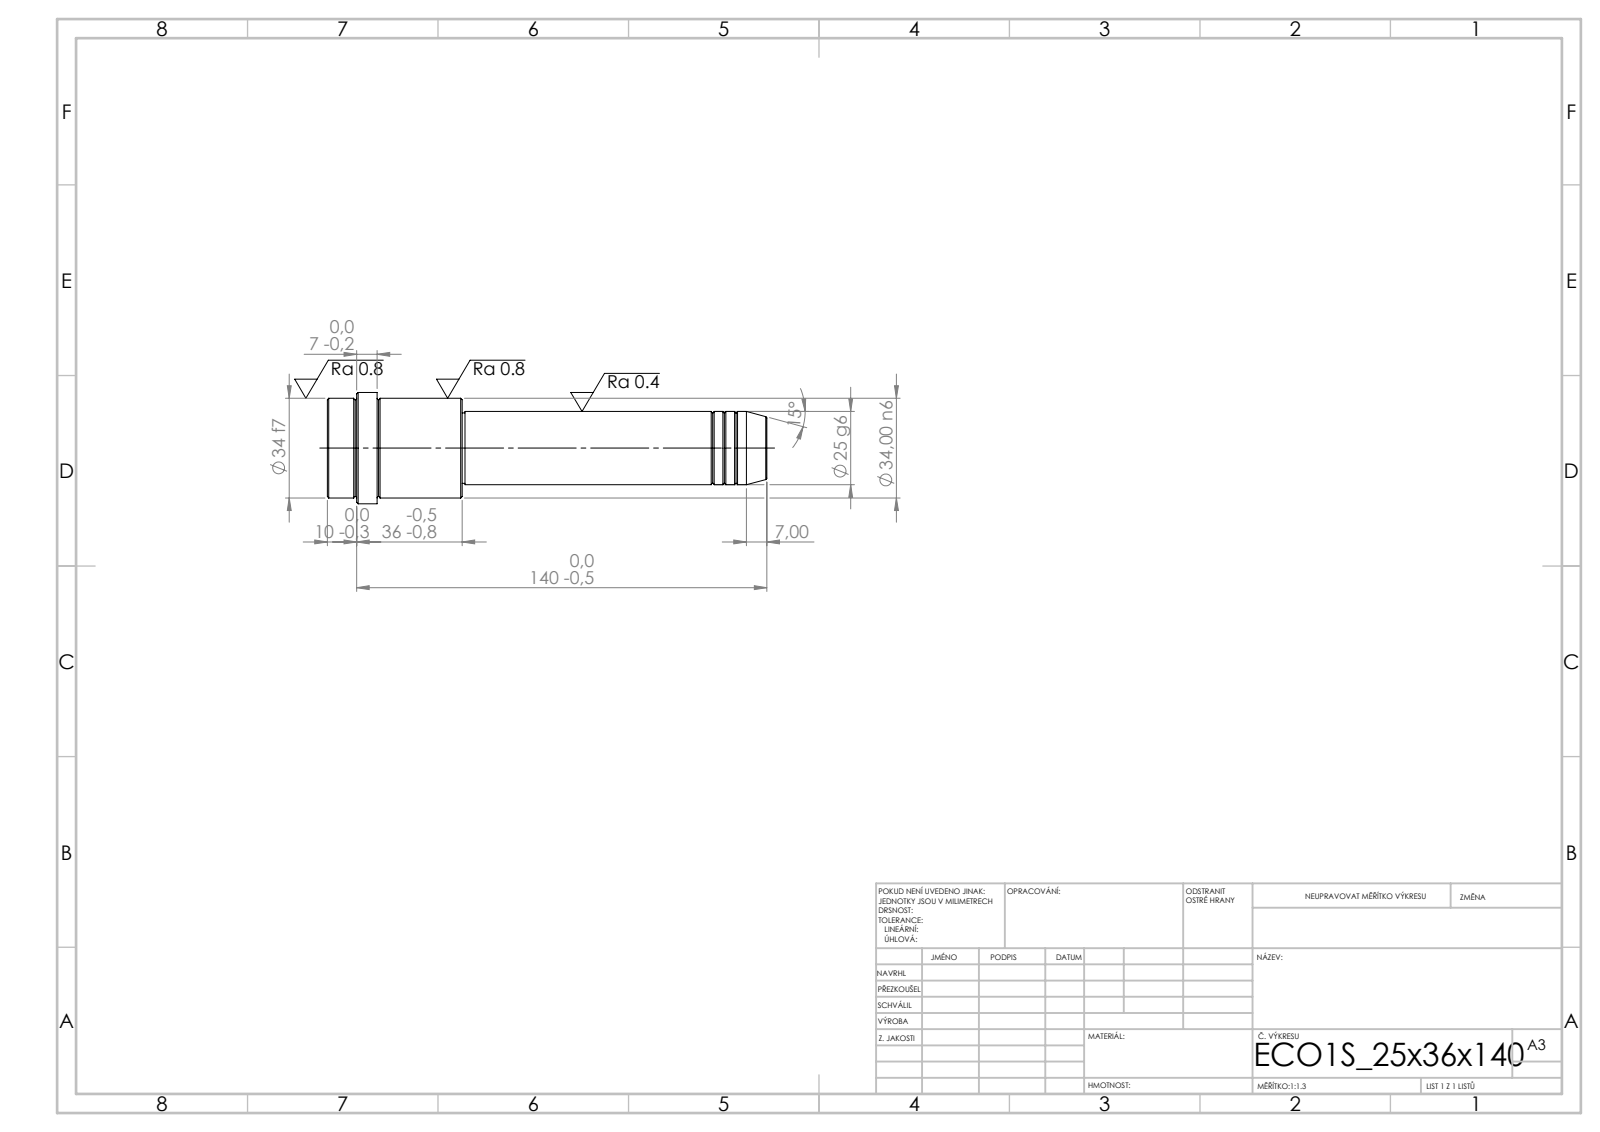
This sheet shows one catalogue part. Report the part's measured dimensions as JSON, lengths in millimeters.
{"step_written_by": "SolidWorks 2019 (CONFIG_CONTROL_DESIGN)", "units": "millimeters", "bodies": {"solids": 1, "faces": 52, "planar": 6, "cylindrical": 16, "other": 30}, "overall_size": [150, 38, 38], "volume_mm3": 93653, "surface_area_mm2": 15487, "round_bosses_or_shafts": [[38, 1], [34, 1], [25, 1], [24, 1]], "face_to_face_distances": [46, 104, 150, 133, 29, 17, 140, 36, 7, 10]}
